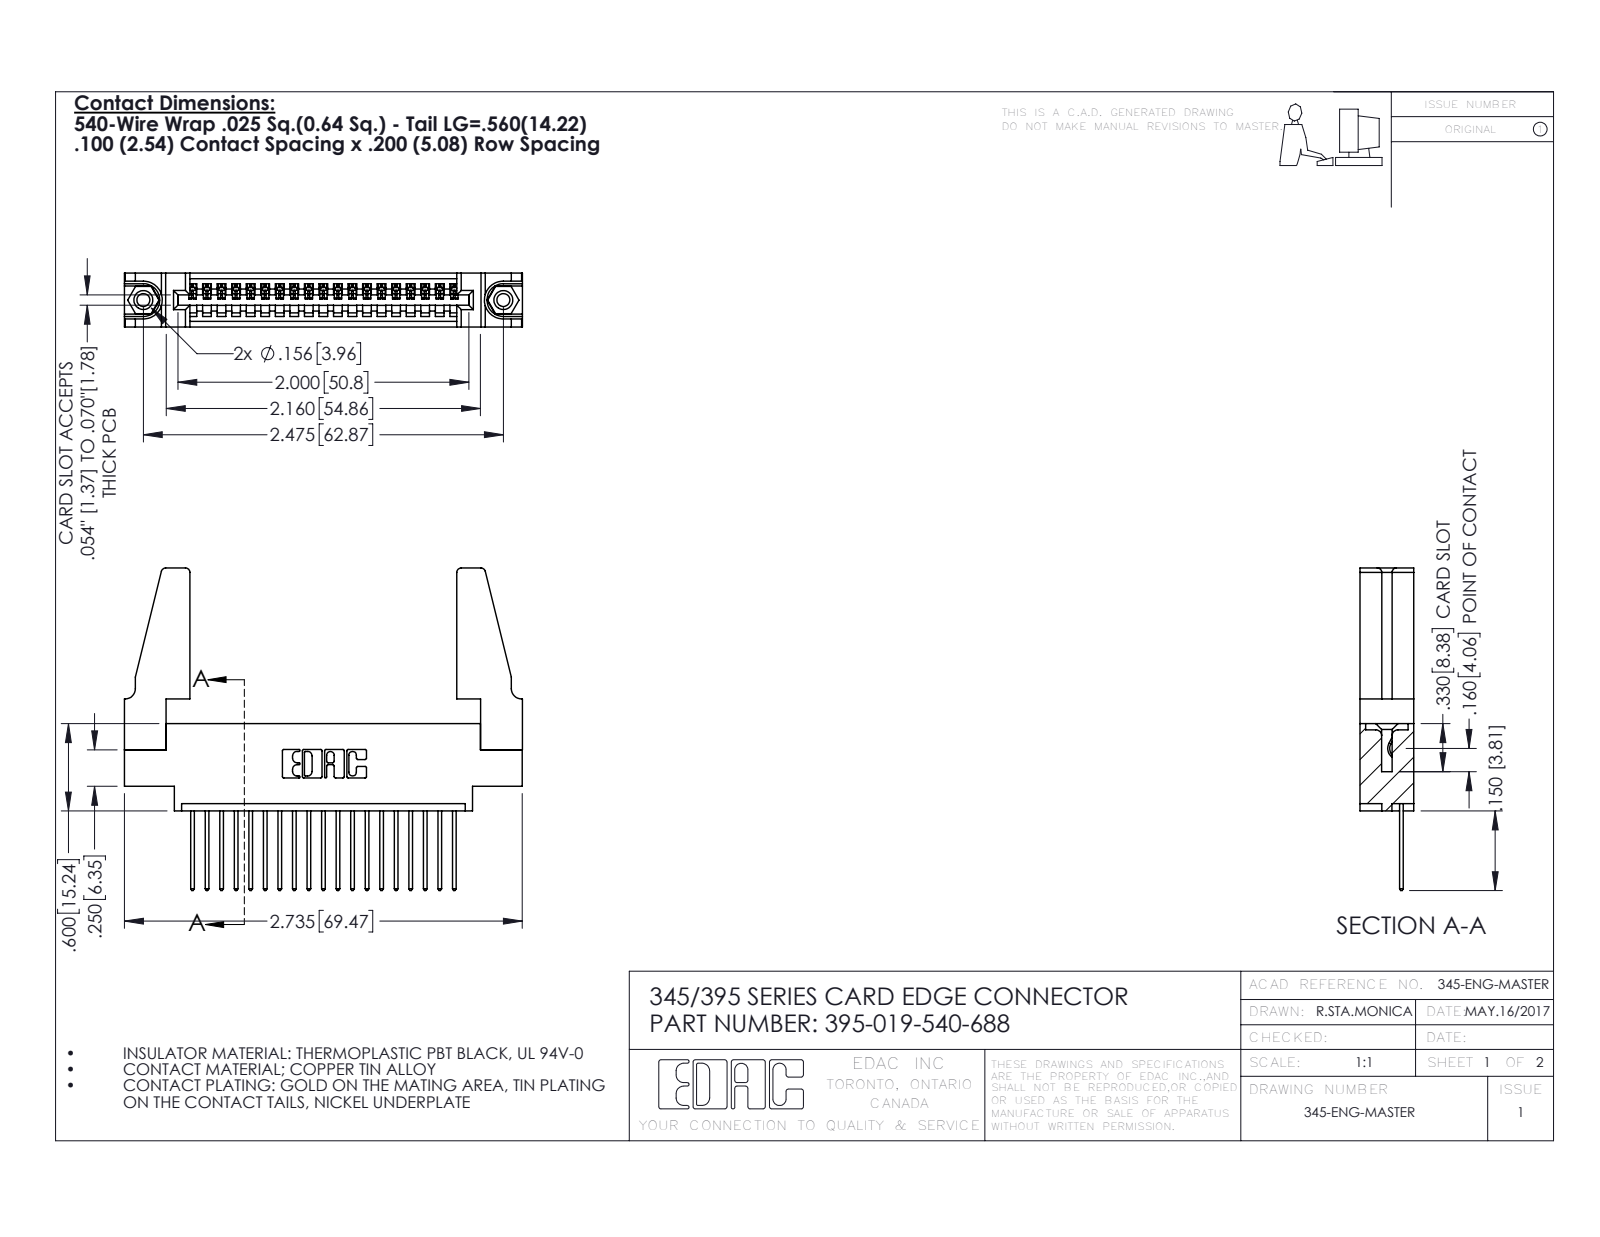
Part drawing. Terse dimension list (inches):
name: 395-019-540-688; 345-292-001_345-293-140; 345-220-078_345-220-088; 345 Part_0.170 Offset - 0.156 Dia-TH (+1 more)
written by: SolidWorks 2016 (CONFIG_CONTROL_DESIGN)
unit: in
bodies: 24 solids, 1356 faces (916 planar, 424 cylindrical, 16 other)
size: 2.736 × 2.217 × 0.37
volume: 0.584 in³; area: 17.88 in²
holes: 2× ⌀0.089, 2× ⌀0.125, 2× ⌀0.156, 1× ⌀0.064
bosses: 2× ⌀0.155
rounds: 38× R0.006, 38× R0.01, 22× R0.01, 8× R0.03, 6× R0.007, 6× R0.031, 3× R0.026, 2× R0.031
face distances: 0.37, 0.072, 0.298, 0.098, 0.272, 0.025, 0.2, 0.225, 0.148, 0.15
hole spacings: 0.27, 2.241, 2.475
